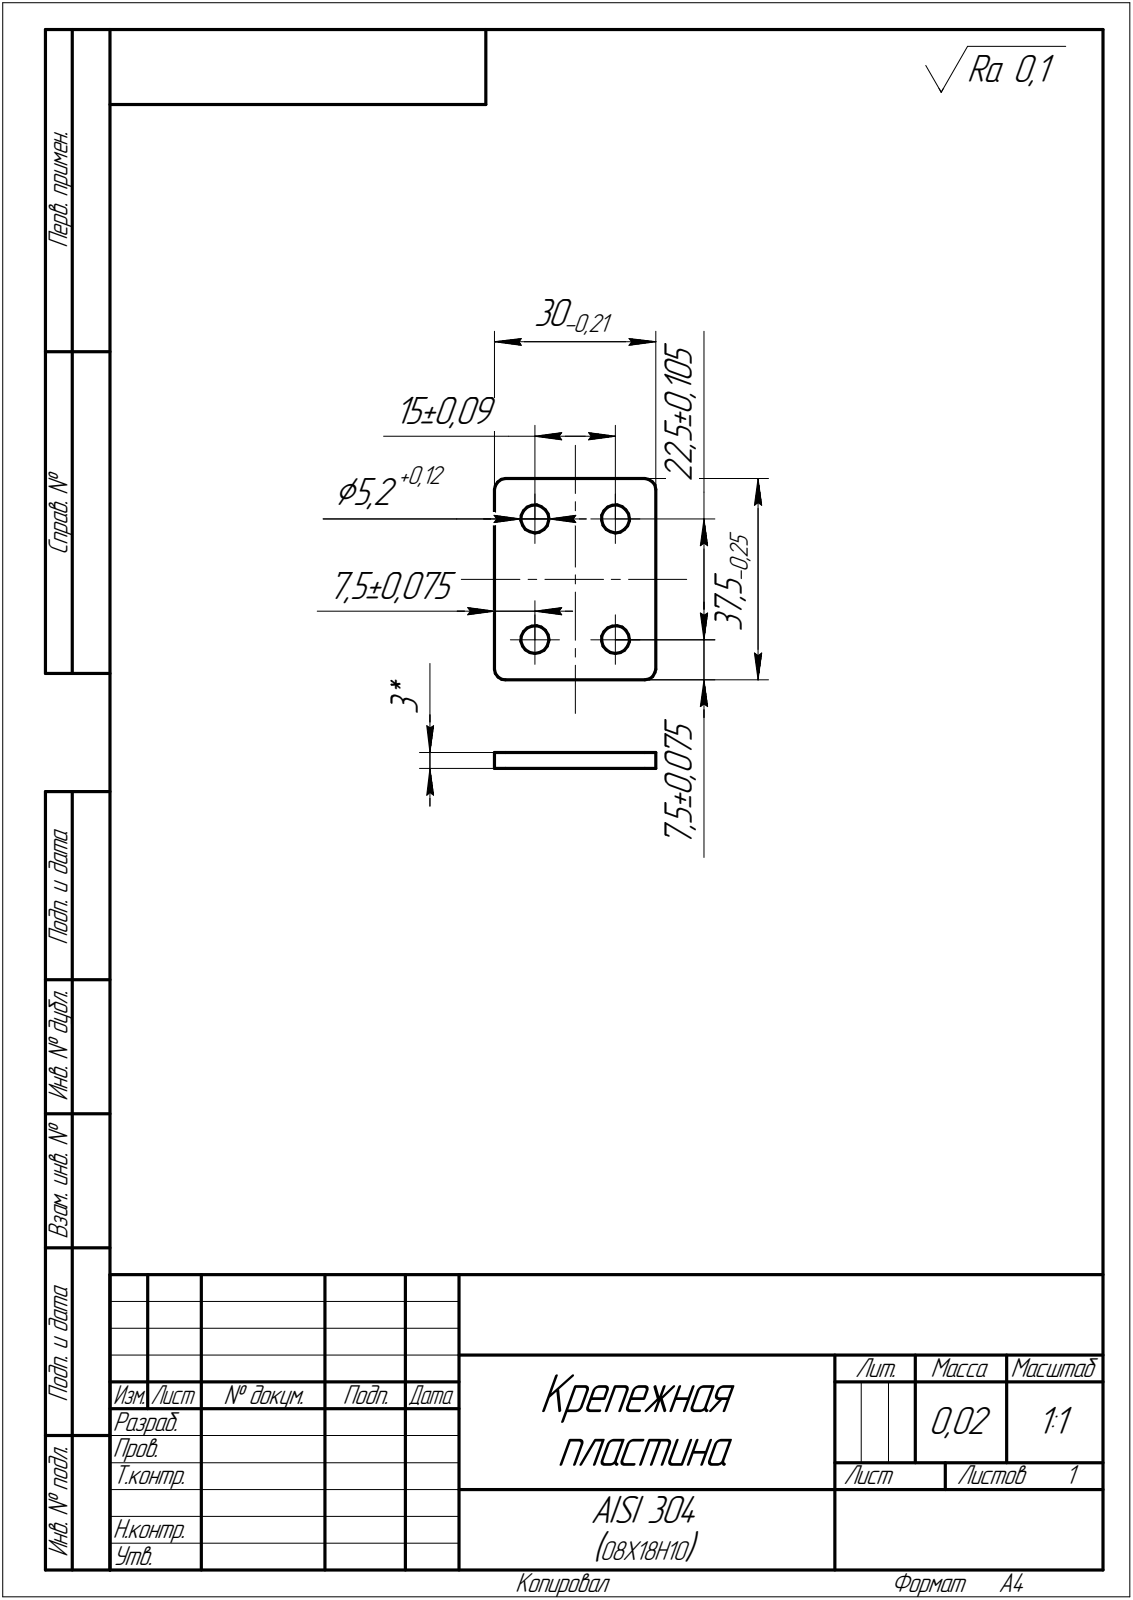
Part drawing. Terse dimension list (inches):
name: Крепежная пластина
written by: ASCON Math Kernel (AUTOMOTIVE_DESIGN)
unit: in
bodies: 1 solid, 14 faces (6 planar, 8 cylindrical, 0 other)
size: 1.476 × 1.181 × 0.118
volume: 0.19 in³; area: 4.129 in²
holes: 4× ⌀0.205
rounds: 4× R0.079
face distances: 0.118, 1.181, 1.476
hole spacings: 0.591, 0.886, 1.065
